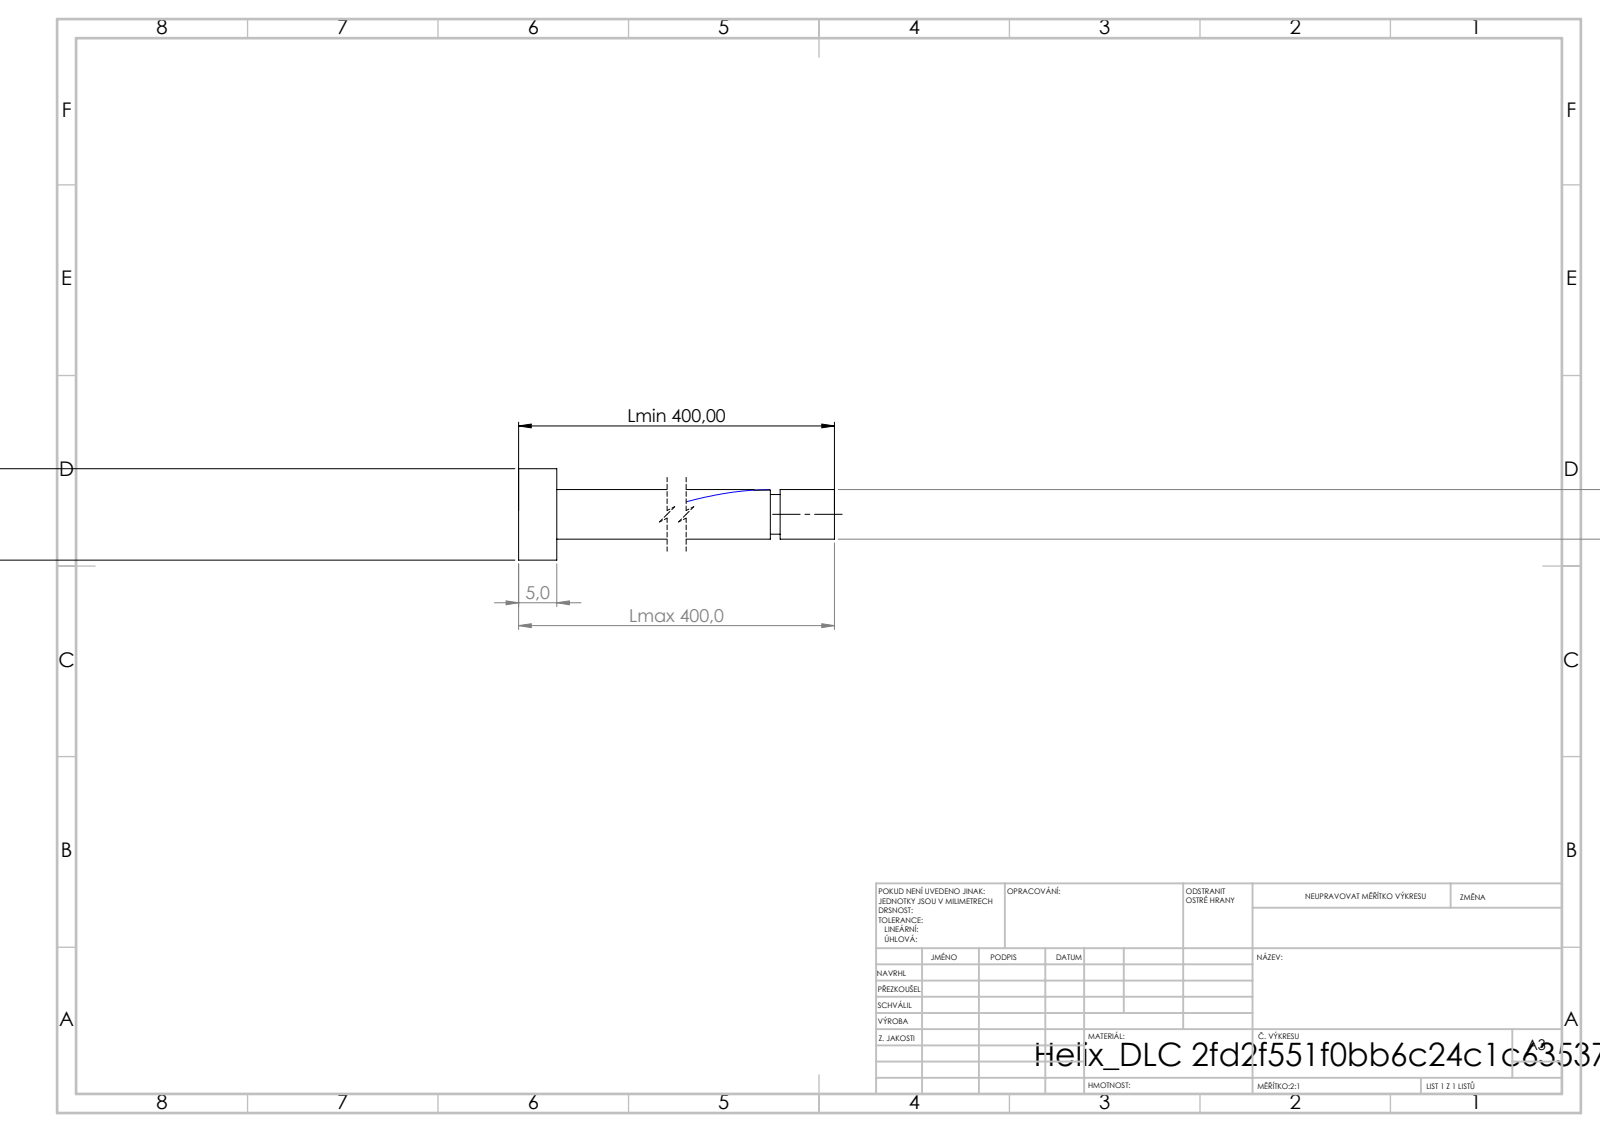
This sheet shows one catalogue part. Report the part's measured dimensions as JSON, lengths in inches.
{"step_written_by": "SolidWorks 2019 (CONFIG_CONTROL_DESIGN)", "units": "inches", "bodies": {"solids": 1, "faces": 16, "planar": 6, "cylindrical": 9, "other": 1}, "overall_size": [15.748, 0.472, 0.472], "volume_in3": 1.006, "surface_area_in2": 17.6, "round_bosses_or_shafts": [[0.472, 1], [0.256, 1], [0.205, 1]], "face_to_face_distances": [0.197, 15.748, 15.551, 15.468, 15.271, 0.28, 15.417, 15.22, 0.051, 0.331]}
